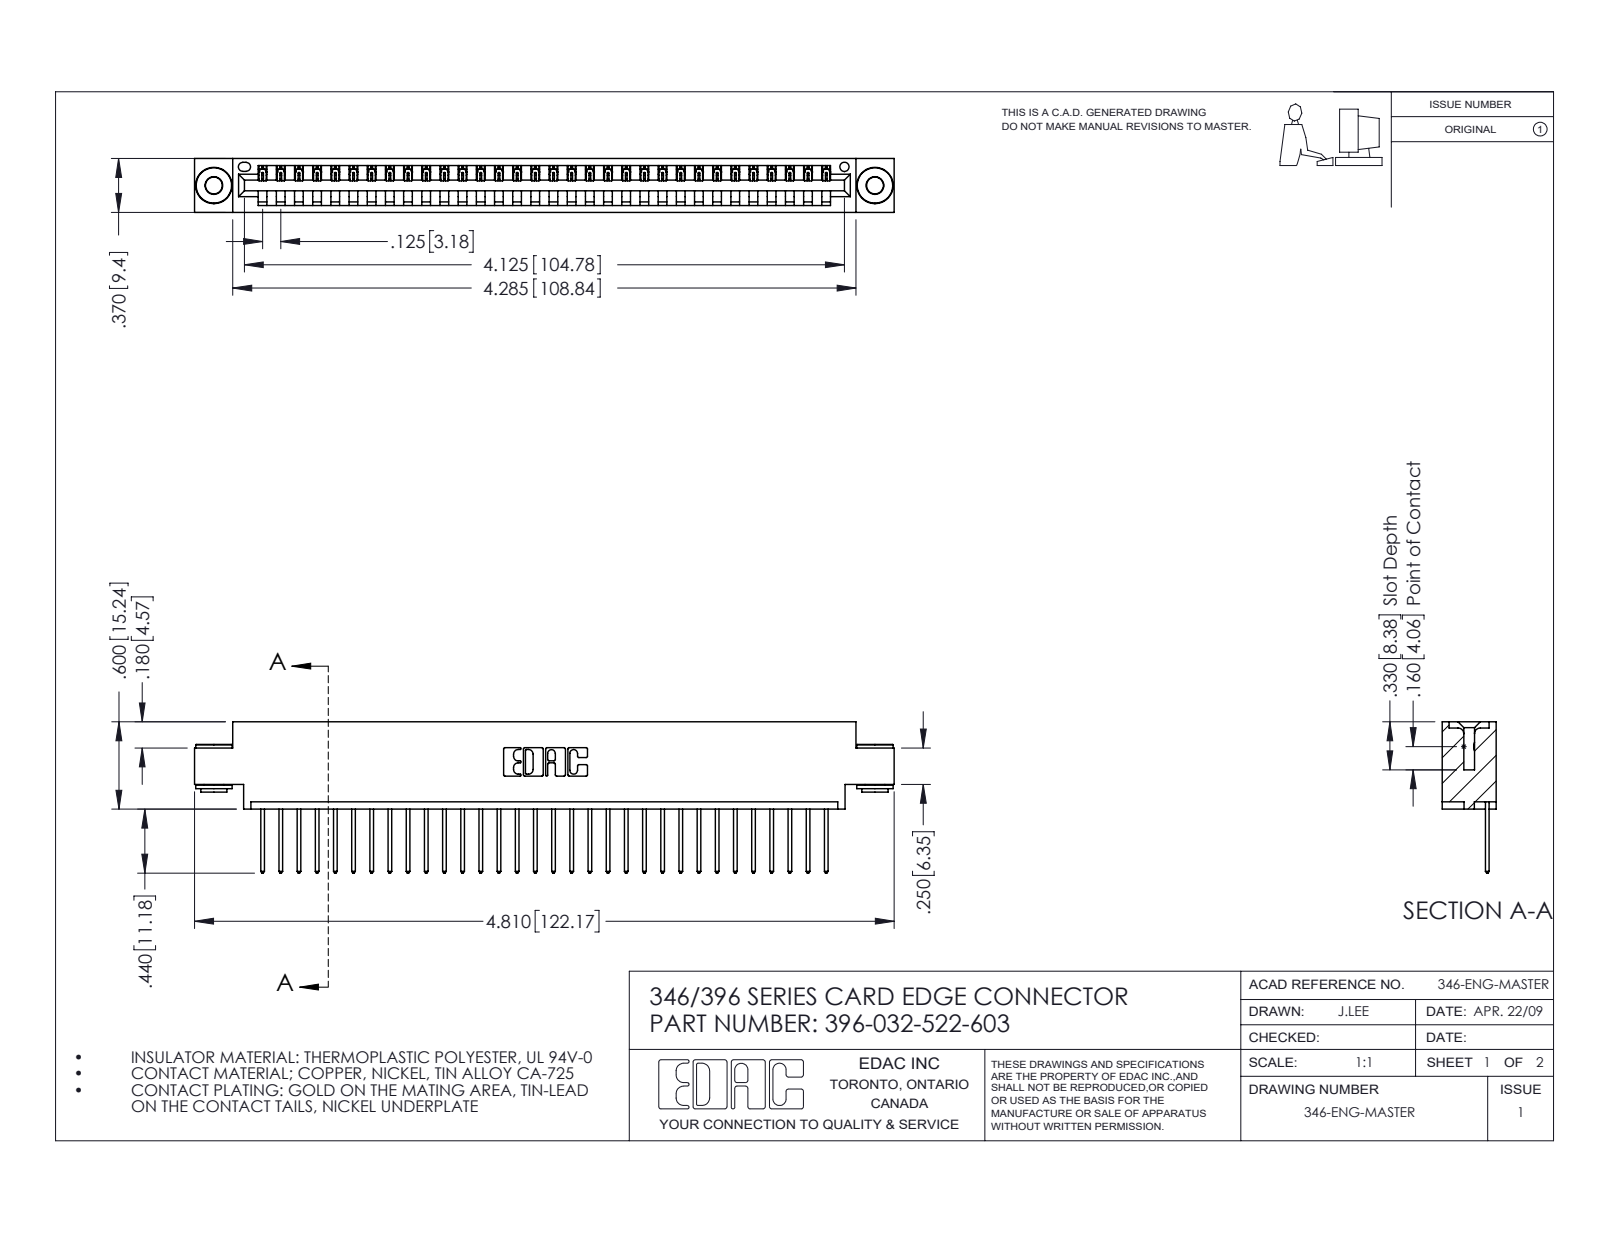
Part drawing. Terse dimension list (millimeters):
name: 345-250-002_345-250-002-102; 396-032-522-603; 346 Part_0.170 Offset - 0.156 Dia-TH; 345-292-001_345-293-122
written by: SolidWorks 2016 (CONFIG_CONTROL_DESIGN)
unit: mm
bodies: 35 solids, 2020 faces (1370 planar, 642 cylindrical, 8 other)
size: 122.2 × 26.4 × 9.4
volume: 11 500 mm³; area: 14 750 mm²
holes: 2× ⌀2.9, 2× ⌀4, 1× ⌀1.6
bosses: 2× ⌀6.4, 2× ⌀4.6, 2× ⌀3.5
rounds: 64× R0.2, 64× R0.3, 22× R0.3, 6× R0.2, 6× R0.8, 3× R0.7, 2× R0.8, 2× R1
face distances: 1.2, 8.2, 9.4, 6.4, 0.6, 1.8, 7.6, 3.8, 5.6, 2.5
hole spacings: 6.2, 110.2, 115.4
